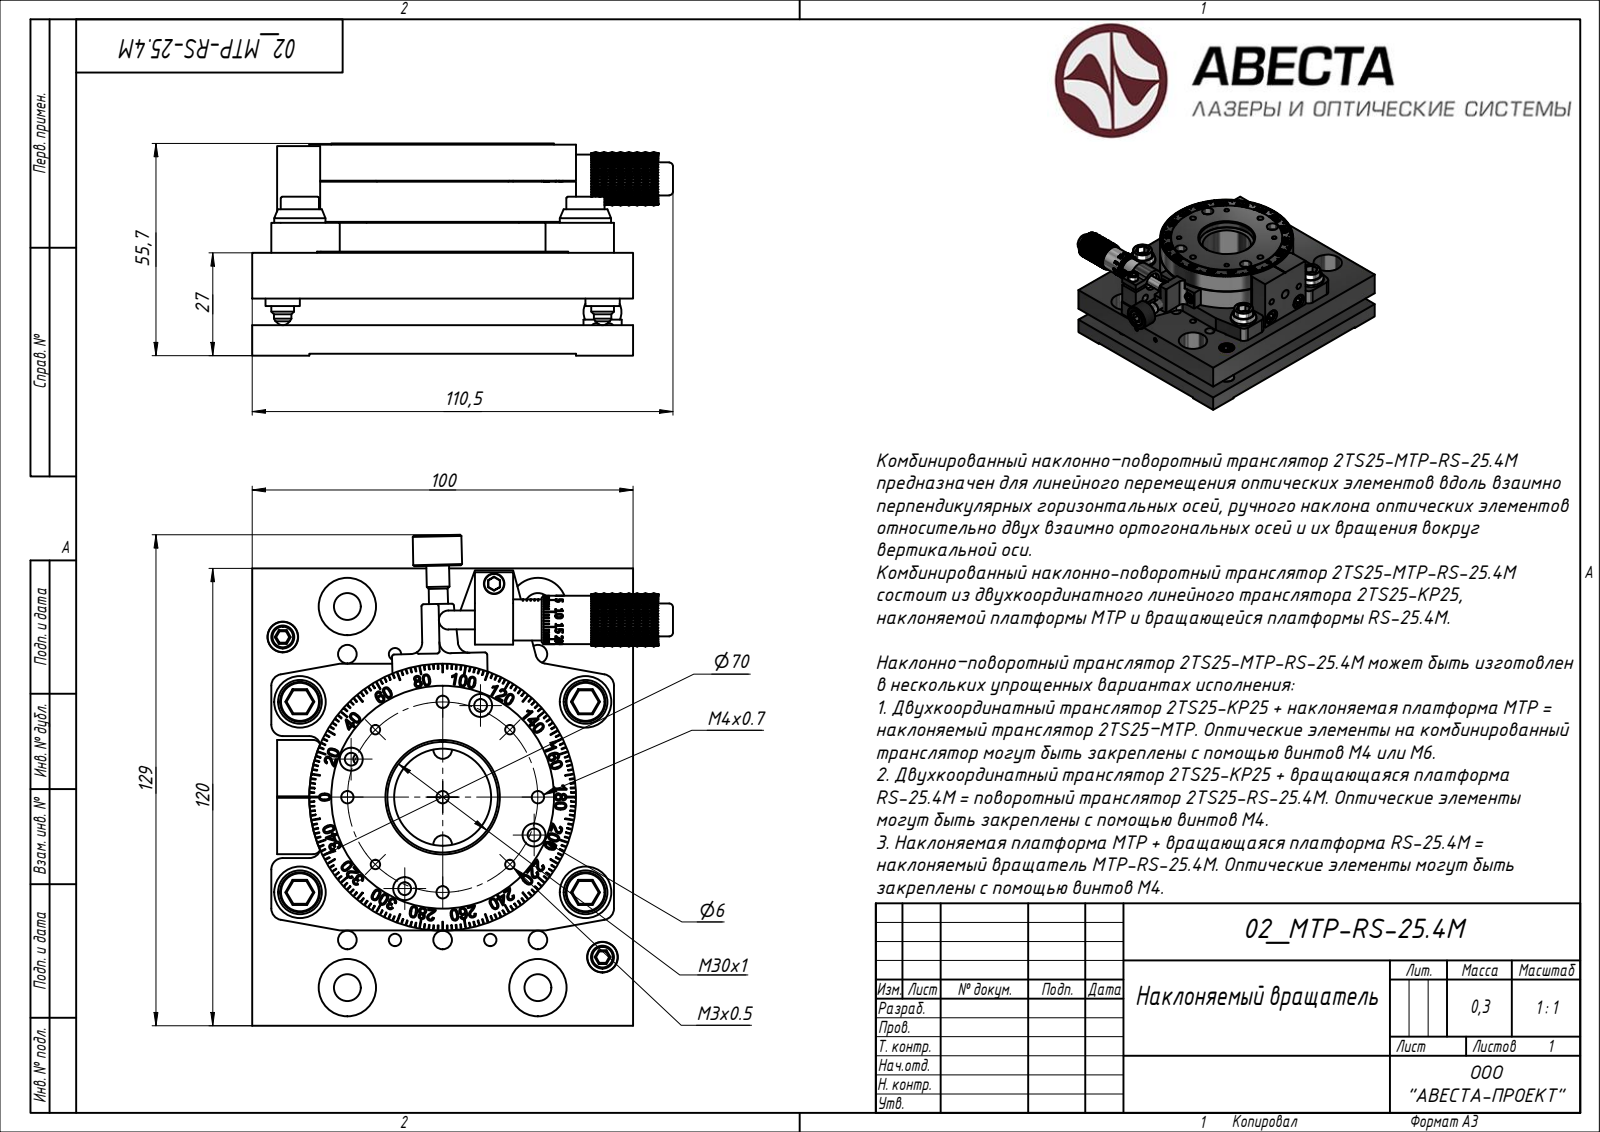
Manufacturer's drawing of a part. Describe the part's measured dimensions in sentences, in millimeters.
Its 3-D file was written by "Rhino 7.34 (AUTOMOTIVE_DESIGN)". It is 55 solids with 6025 faces: 4460 planar, 685 cylindrical and 880 other. Overall it measures 128.81 by 110.5 by 55.7 millimeters. Its volume is 326 242 cubic millimeters and its surface area 129 063 square millimeters. Round holes: 21 of diameter 3.24, 19 of diameter 6, 16 of diameter 4.92, 6 of diameter 2.01, 6 of diameter 2.8, 6 of diameter 3.4, 6 of diameter 5, 5 of diameter 2.46, 5 of diameter 7, 4 of diameter 2.2, 4 of diameter 10.5, 4 of diameter 15. Round bosses or shafts: 8 of diameter 2.5, 7 of diameter 2, 6 of diameter 4.5, 5 of diameter 13.5, 5 of diameter 6, 4 of diameter 10, 4 of diameter 5.4, 4 of diameter 3. Partial cylindrical surfaces (rounded edges, fillets, slot ends): 15 of radius 3, 9 of radius 0.64, 8 of radius 3.25, 7 of radius 0.5, 6 of radius 1.1, 4 of radius 1.25, 3 of radius 1.23, 3 of radius 1.23. The main face-to-face distances are 19, 26.5, 7.5, 7, 12, 14.5, 7.9, 34.4, 26.9, 19.9. The hole center spacings are 15.5, 10, 25, 28.35, 35.36, 42.41, 50.02, 19.14.
